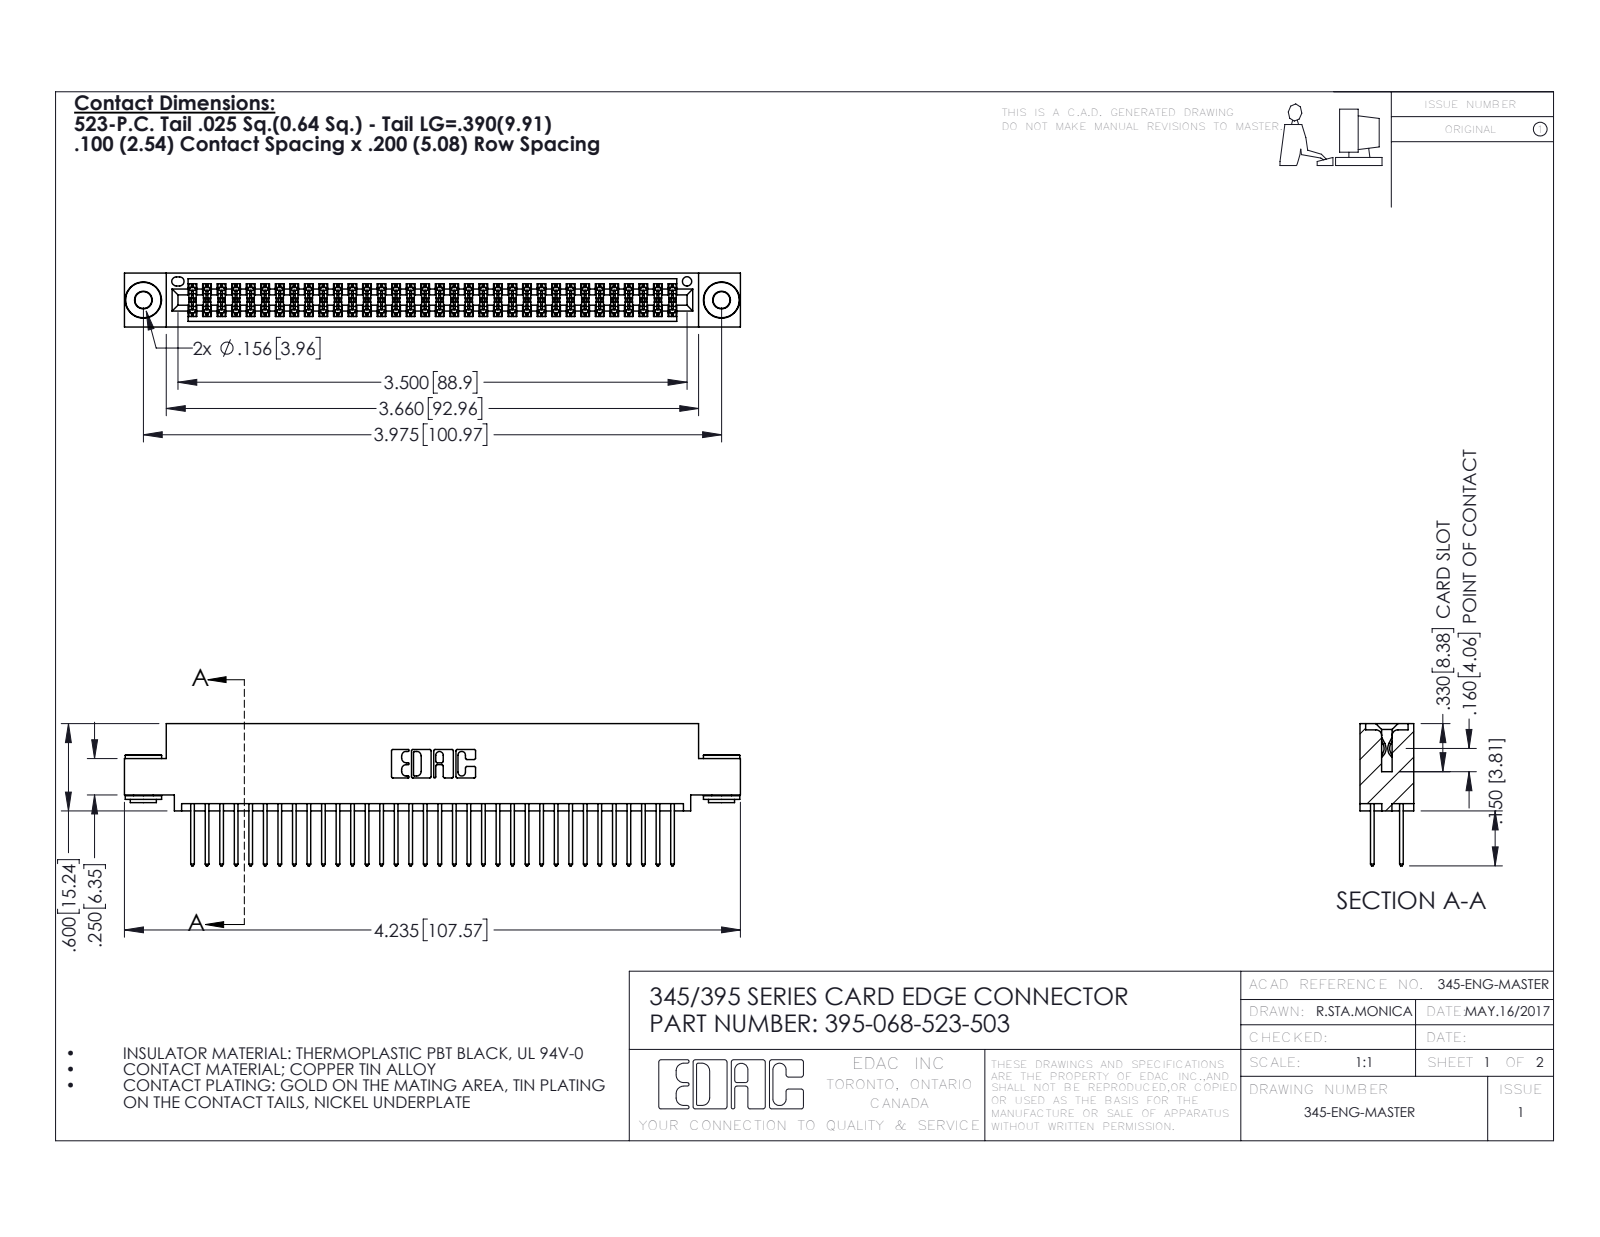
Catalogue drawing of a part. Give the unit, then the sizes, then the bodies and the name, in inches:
Units: inches
Overall size (bounding box): 4.235 × 0.977 × 0.37
Round holes (diameter × count): ⌀0.116 ×2, ⌀0.156 ×2, ⌀0.064 ×1
Round bosses / shafts (diameter × count): ⌀0.25 ×2, ⌀0.18 ×2, ⌀0.136 ×2
Partial cylindrical surfaces — rounded edges, fillets, slot ends (radius × count): R0.006 ×102, R0.01 ×68, R0.01 ×22, R0.007 ×6, R0.031 ×6, R0.026 ×3, R0.014 ×2, R0.019 ×2
Main face-to-face distances: 0.072, 0.298, 0.2, 0.025, 0.098, 0.272, 0.37, 0.225, 0.175, 0.149
Hole centre spacings: 0.27, 3.74, 3.975
Volume: 0.638 in³ · Surface area: 25.16 in²
Bodies: 71 solids, 3568 faces (2338 planar, 1222 cylindrical, 8 other)
Part name (STEP PRODUCT): 345 Part_0.110 Offset - 0.156 Dia-TH; 345-250-002_345-250-002-102; 345-292-001_345-293-123; 395-068-523-503
STEP written by: SolidWorks 2016 (CONFIG_CONTROL_DESIGN)
